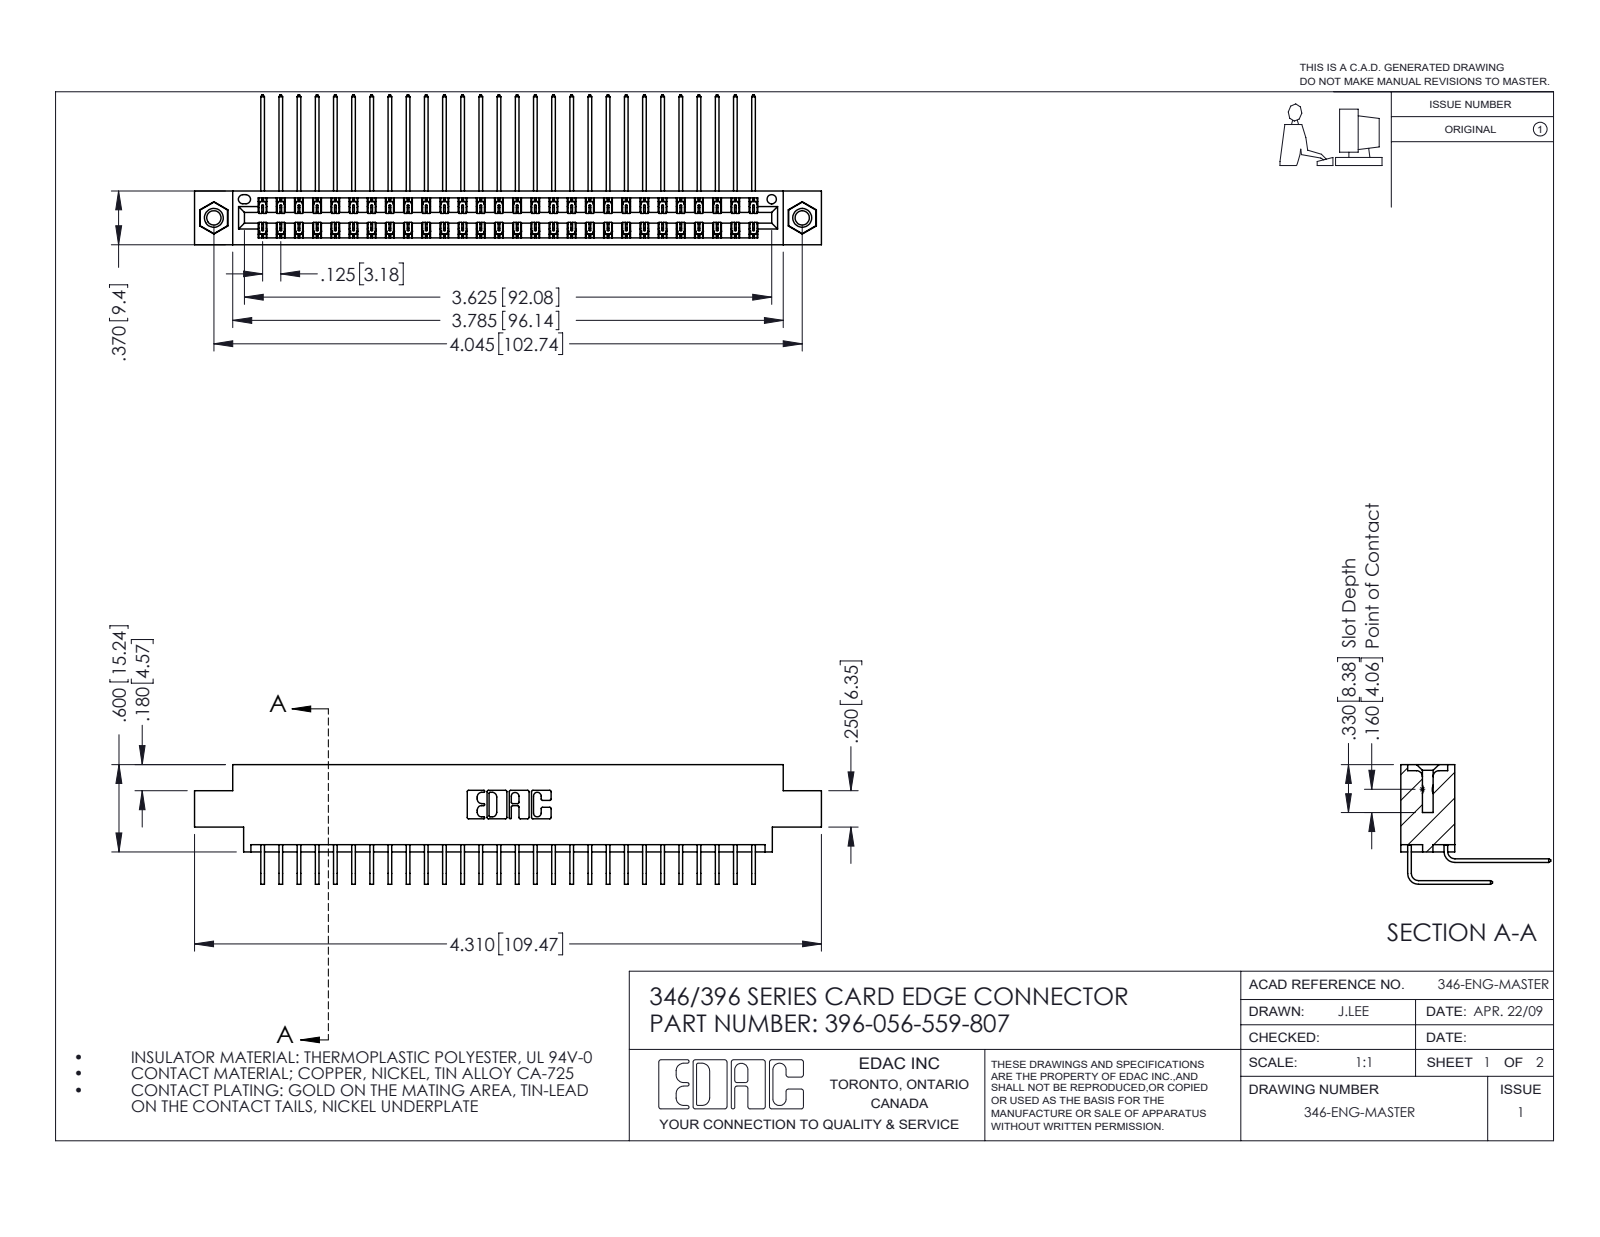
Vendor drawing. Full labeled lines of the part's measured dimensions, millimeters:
Part name (STEP PRODUCT): 345-292-001_559 Tail - 2; 396-056-559-807; 345-250-001_345-250-005-103; 346 Part_0.170 Offset - 0.156 Dia-TI (+1 more)
STEP written by: SolidWorks 2016 (CONFIG_CONTROL_DESIGN)
Units: millimetres
Bodies: 59 solids, 3210 faces (2184 planar, 1010 cylindrical, 16 other)
Overall size (bounding box): 109.5 × 26.2 × 20.9
Volume: 10 700 mm³ · Surface area: 16 280 mm²
Round holes (diameter × count): ⌀2.5 ×2, ⌀3.2 ×2, ⌀4 ×2, ⌀1.6 ×1
Round bosses / shafts (diameter × count): ⌀3.9 ×2
Partial cylindrical surfaces — rounded edges, fillets, slot ends (radius × count): R0.2 ×84, R0.3 ×22, R0.2 ×6, R0.8 ×6, R0.7 ×3, R0.4 ×2, R0.6 ×2, R0.6 ×2
Main face-to-face distances: 1.2, 8.2, 0.6, 9.4, 6.4, 1.8, 7.6, 7, 5.6, 3.8
Hole centre spacings: 6.2, 97.5, 102.7
